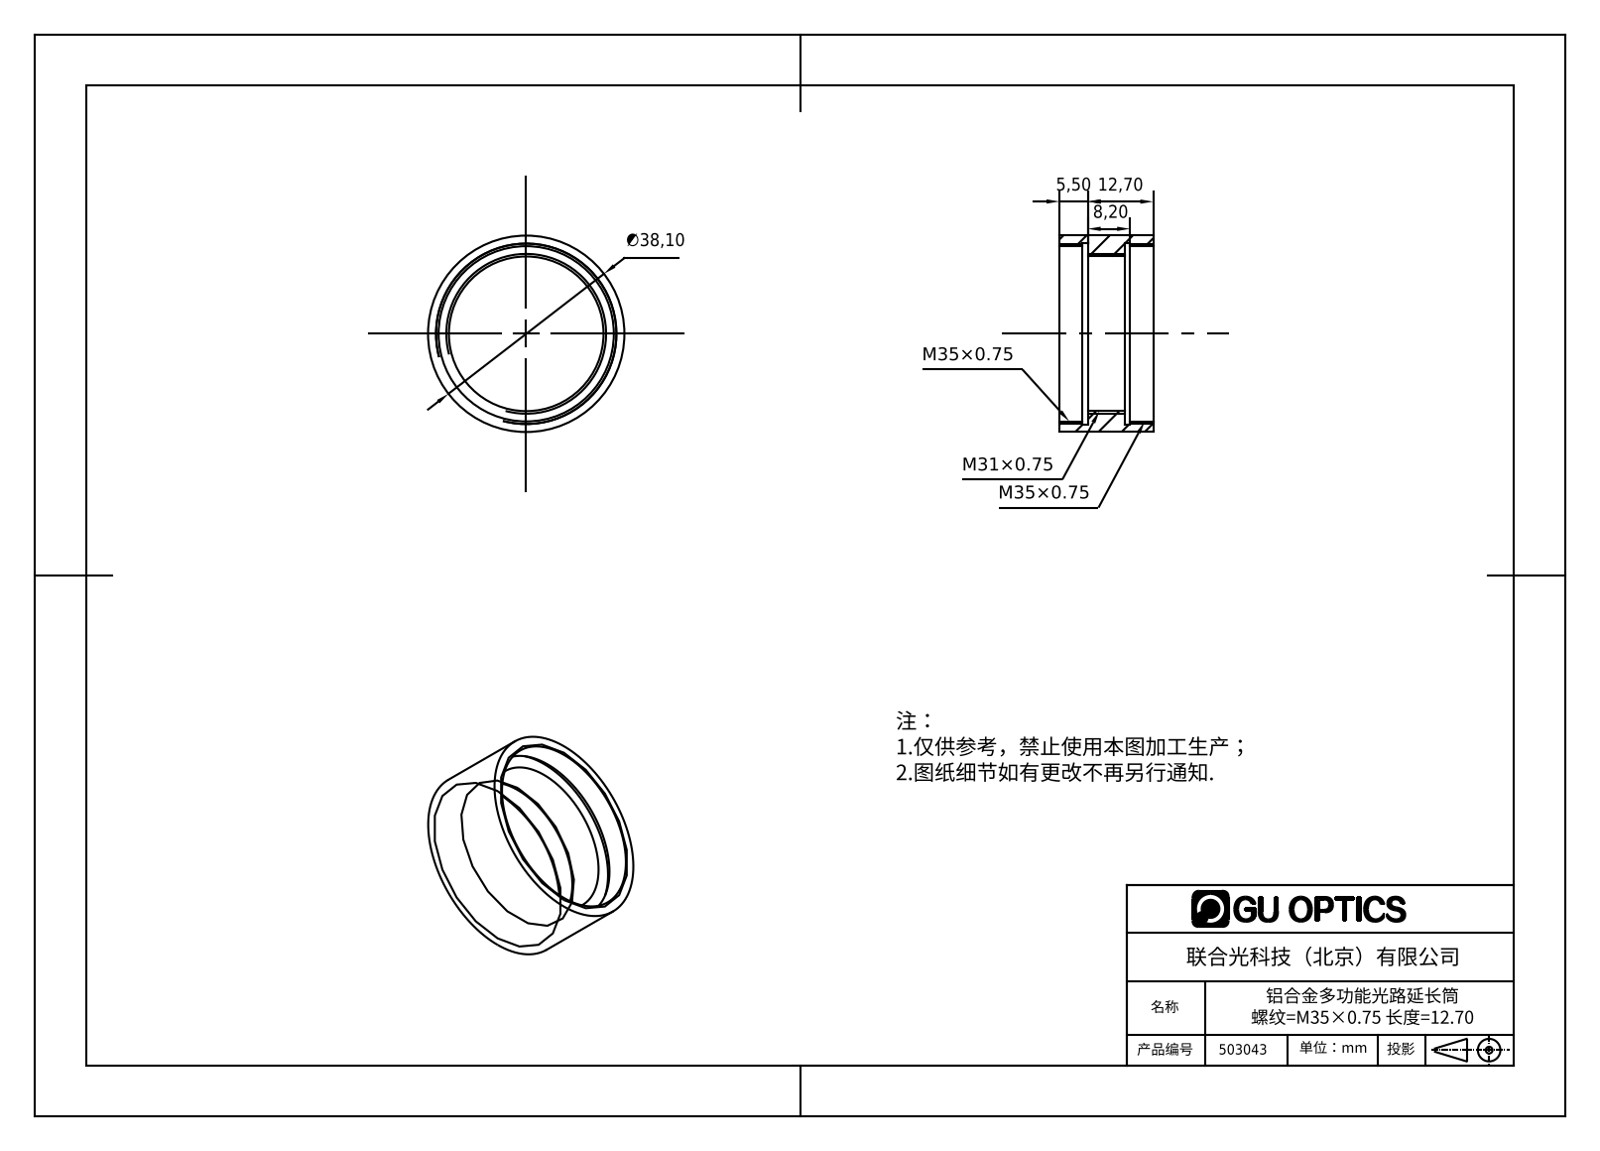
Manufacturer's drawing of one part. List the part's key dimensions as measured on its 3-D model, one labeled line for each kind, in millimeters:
Part name (STEP PRODUCT): 503043
STEP written by: SolidWorks 2016 (AUTOMOTIVE_DESIGN)
Units: millimetres
Bodies: 1 solid, 18 faces (6 planar, 12 cylindrical, 0 other)
Overall size (bounding box): 38.1 × 38.1 × 18.2
Volume: 5 543 mm³ · Surface area: 5 167 mm²
Round holes (diameter × count): ⌀30 ×1, ⌀34 ×1, ⌀35.2 ×1
Round bosses / shafts (diameter × count): ⌀38.1 ×1
Main face-to-face distances: 5.5, 12.7, 7.2, 18.2, 4.5, 13.7, 1, 8.2, 9.2
